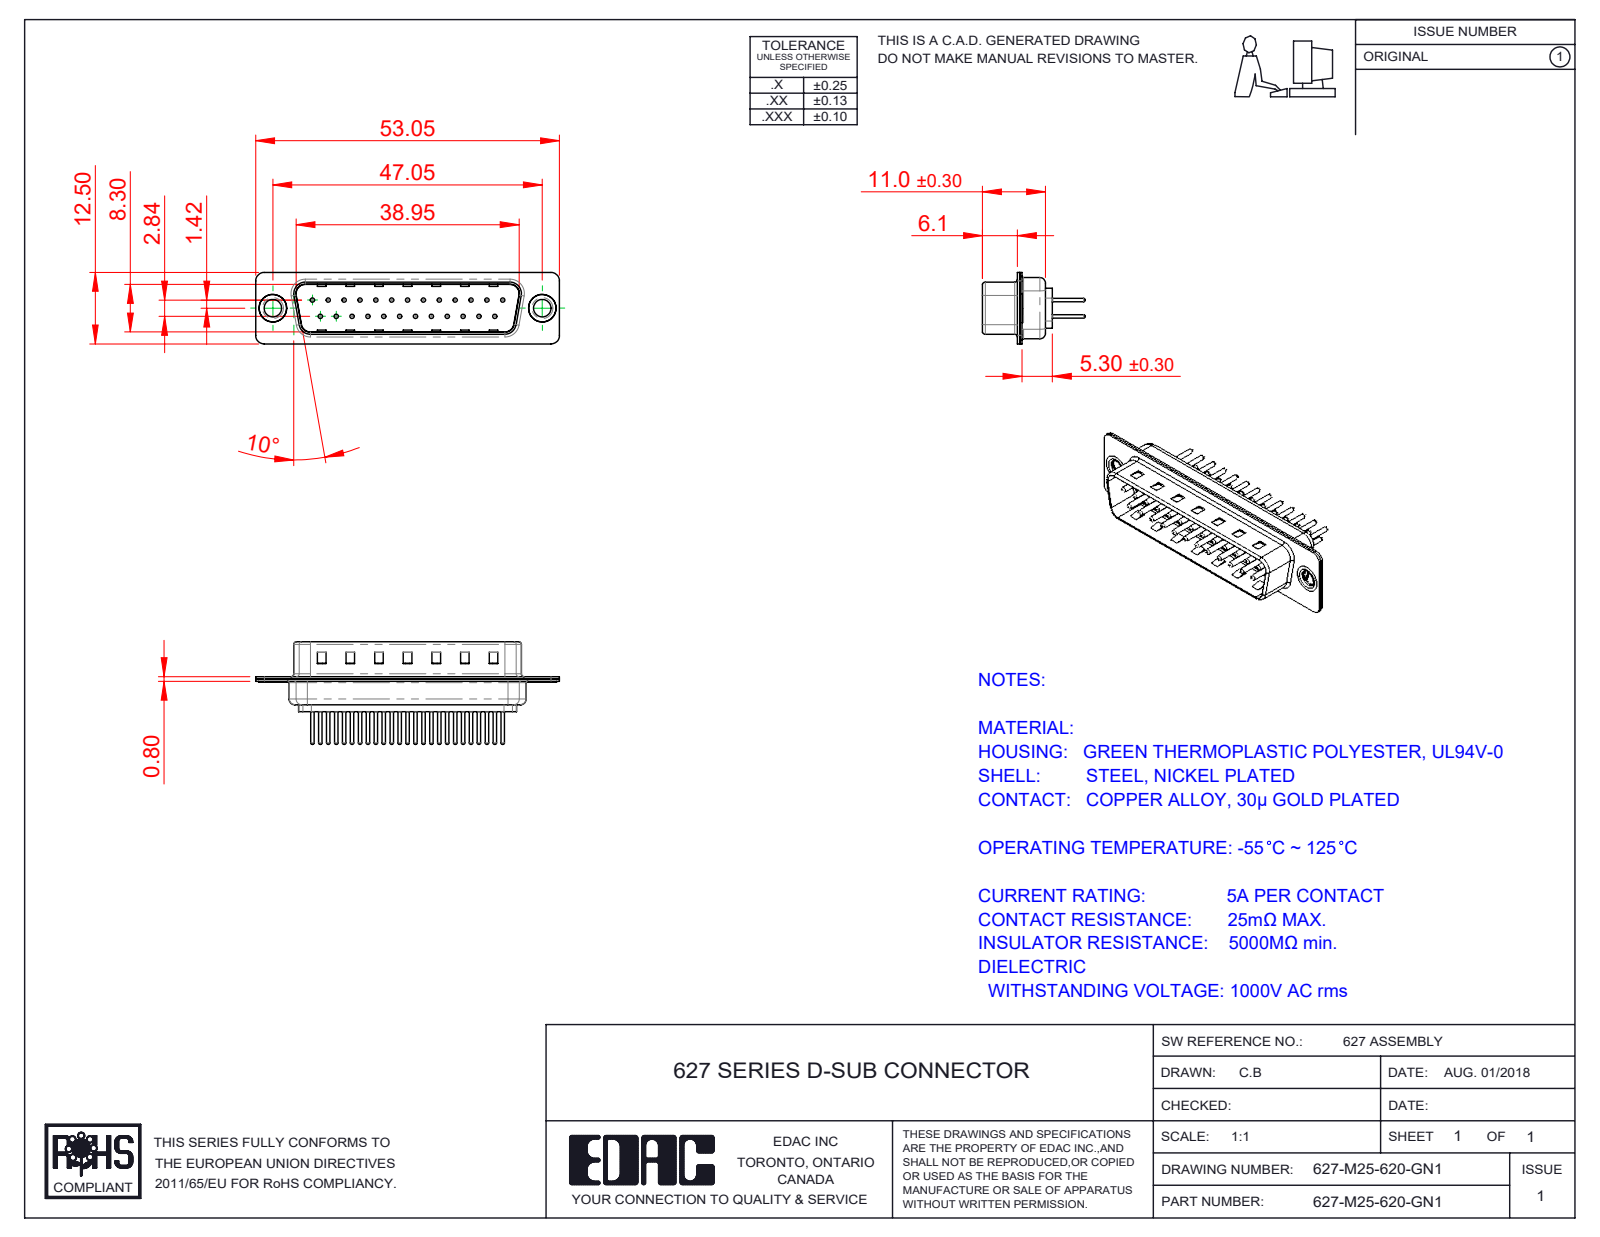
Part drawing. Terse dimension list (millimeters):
name: 627M Housing_25 Contacts; 627M Contact Row 2_20; 627-M25-620-GN1; 627M Thru Hole Rivet (+3 more)
written by: SolidWorks 2020 (CONFIG_CONTROL_DESIGN)
unit: mm
bodies: 30 solids, 1275 faces (346 planar, 471 cylindrical, 458 other)
size: 53.05 × 17.9 × 12.5
volume: 2 641 mm³; area: 6 698 mm²
holes: 25× ⌀0.75, 25× ⌀1.6, 25× ⌀2, 2× ⌀3.05, 2× ⌀4, 2× ⌀4.8
bosses: 25× ⌀1.5, 25× ⌀0.6, 2× ⌀5, 2× ⌀4.9, 2× ⌀3.55
rounds: 16× R1.5, 12× R2, 8× R0.5, 8× R1.6, 4× R0.25, 4× R0.6, 4× R0.65, 4× R0.9
face distances: 0.4, 0.8, 9.5, 9.1, 8.7, 9.9, 1.2, 6.1, 5.7, 0.75
hole spacings: 3.16, 2.77, 5.54, 8.31, 11.08, 13.85, 16.62, 5.03
